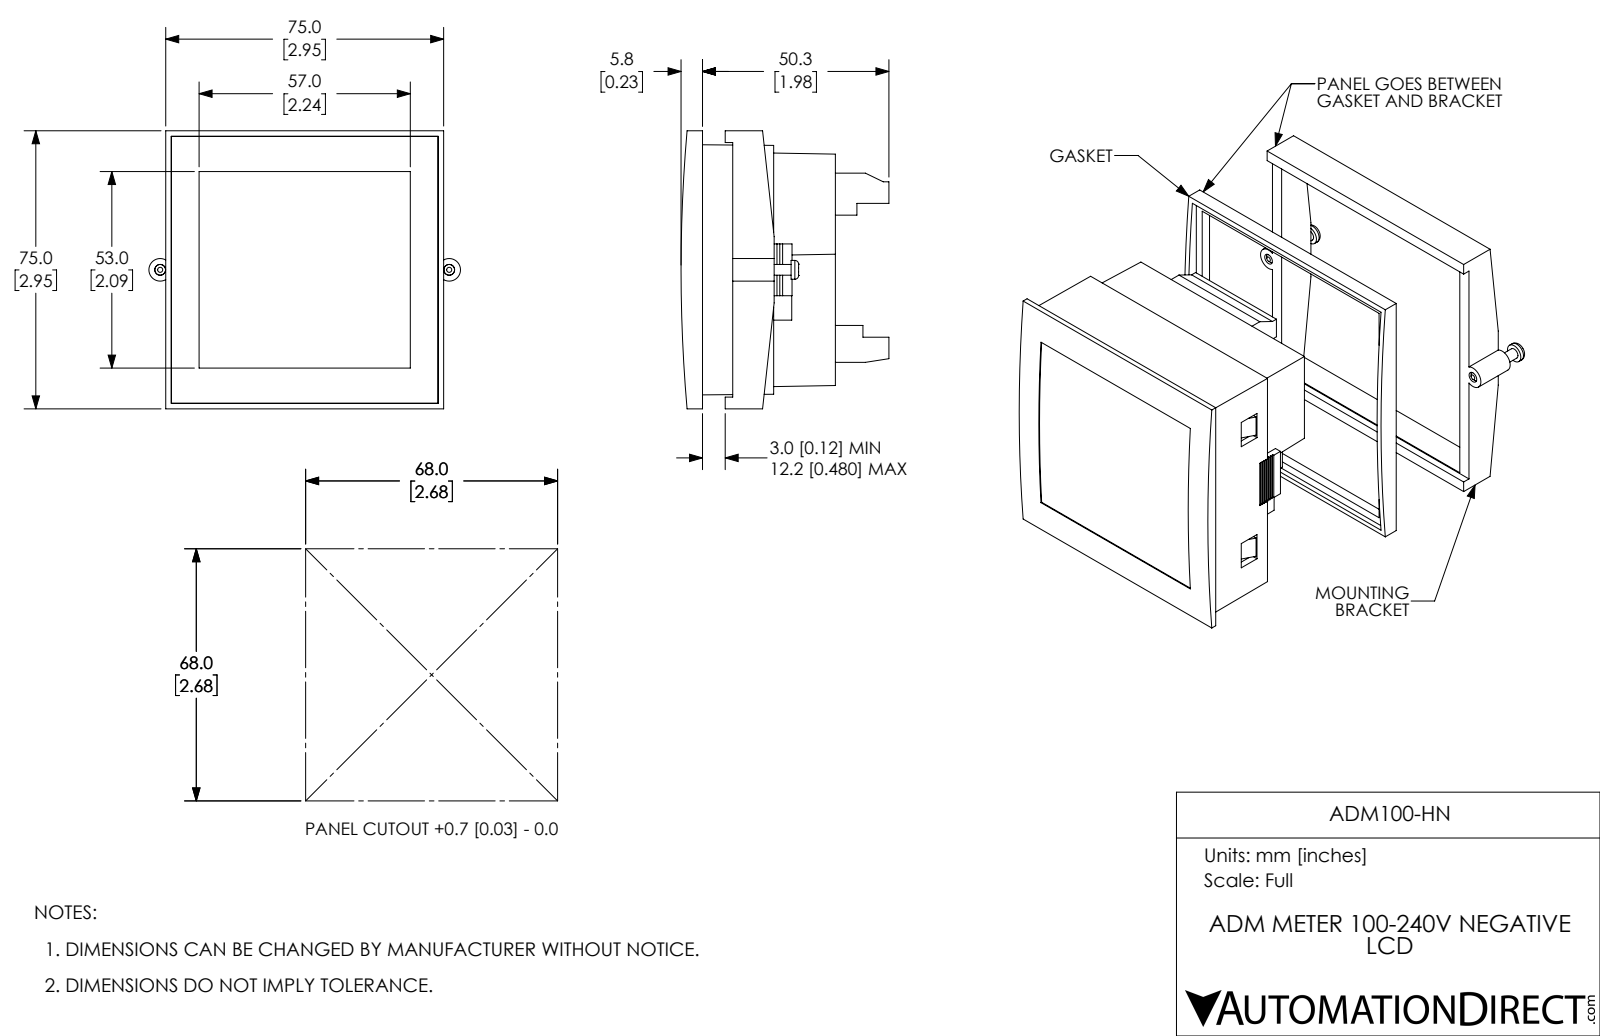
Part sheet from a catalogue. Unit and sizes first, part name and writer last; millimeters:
Units: millimetres
Overall size (bounding box): 84.1 × 75 × 56.1
Round holes (diameter × count): ⌀3.8 ×13, ⌀2.9 ×2
Round bosses / shafts (diameter × count): ⌀3.8 ×13, ⌀5.1 ×2, ⌀2.9 ×2
Partial cylindrical surfaces — rounded edges, fillets, slot ends (radius × count): R3 ×2, R432.7 ×2
Main face-to-face distances: 1.9, 7.7, 6, 69, 67.5, 2.3, 3.8, 71.2, 65.6, 29
Hole centre spacings: 42, 5.1, 42.6, 10.2, 43.8, 15.2, 45.5, 20.3
Volume: 156 700 mm³ · Surface area: 58 480 mm²
Bodies: 23 solids, 419 faces (335 planar, 76 cylindrical, 8 other)
Part name (STEP PRODUCT): ADM100-HN
STEP written by: SolidWorks 2017 (AUTOMOTIVE_DESIGN)
